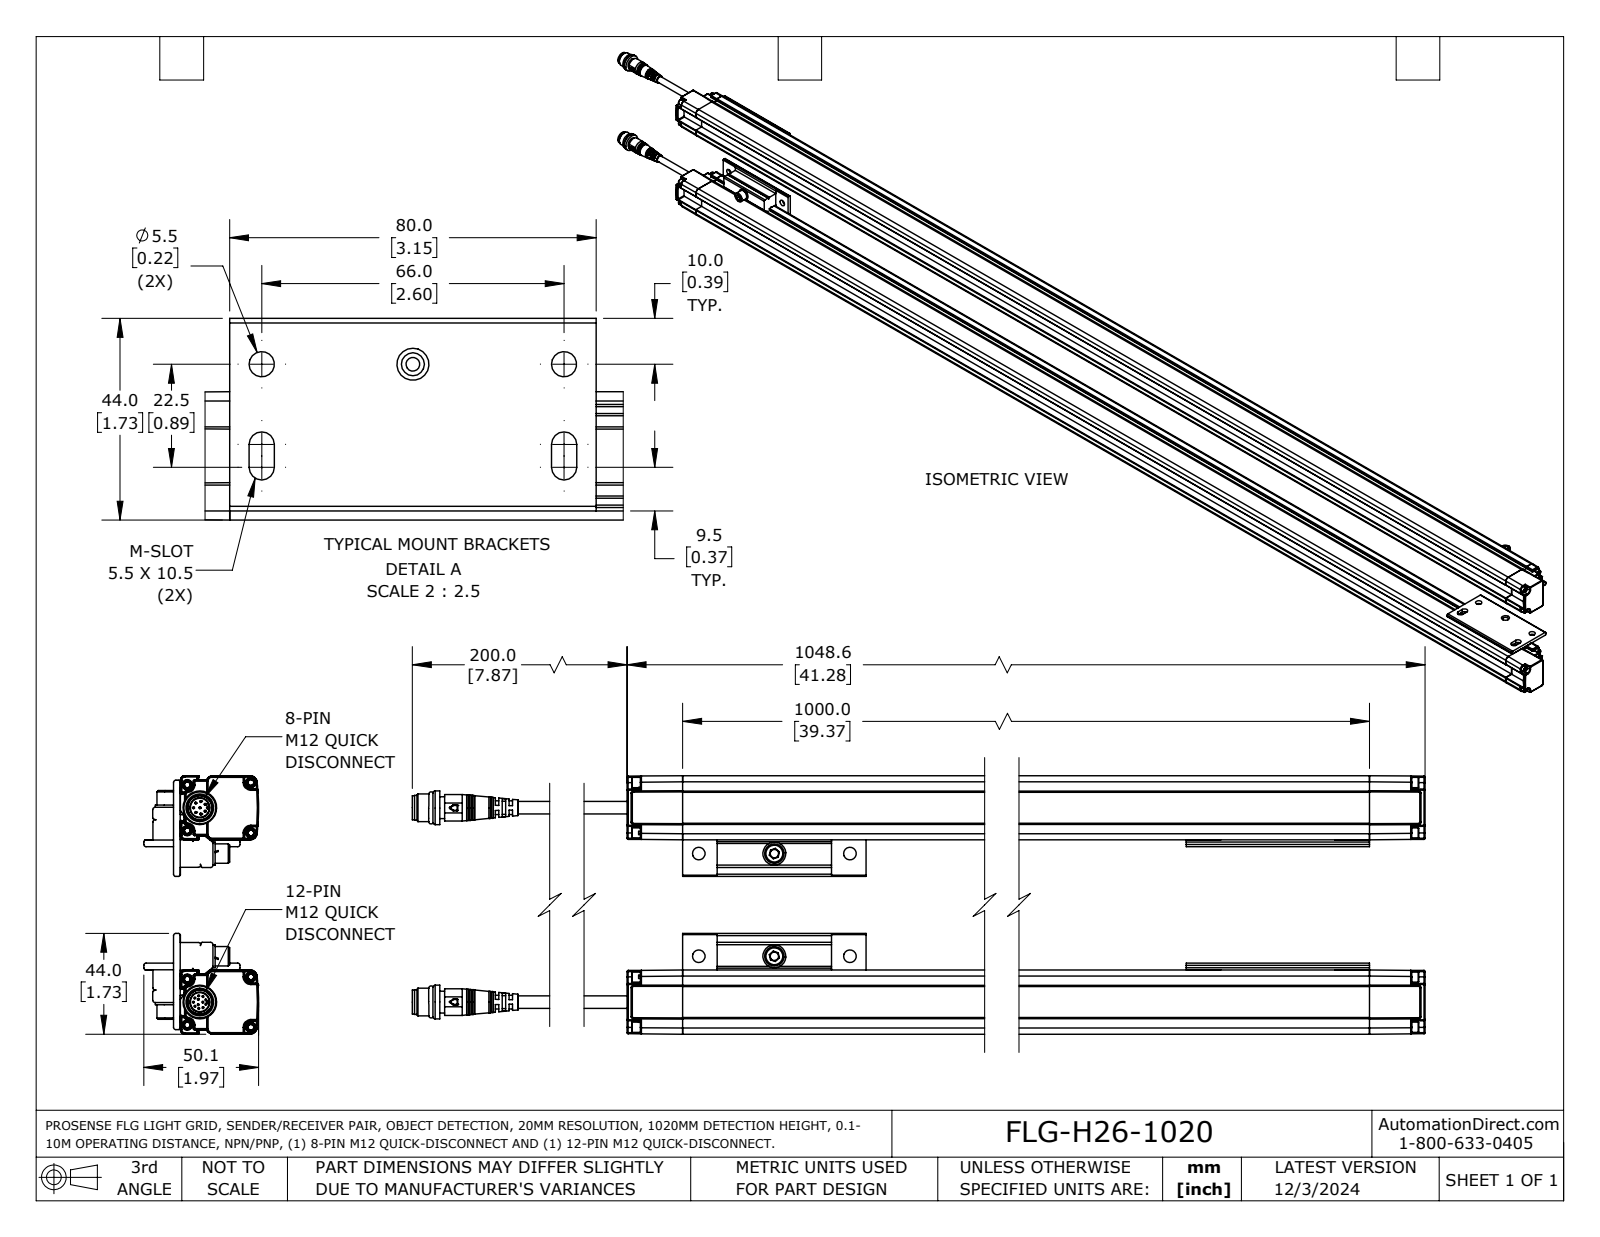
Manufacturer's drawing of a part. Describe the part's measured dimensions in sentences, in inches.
The part is named "FLG-H26-1020". Its 3-D file was written by "SolidWorks 2023 (AUTOMOTIVE_DESIGN)". It is 10 solids with 1668 faces: 816 planar, 456 cylindrical and 396 other. Overall it measures 44.904 by 4.441 by 1.972 inches. Its volume is 103.7 cubic inches and its surface area 658.6 square inches. Round holes: 16 of diameter 0.016, 6 of diameter 0.217, 4 of diameter 0.098, 3 of diameter 0.197, 2 of diameter 0.327. Round bosses or shafts: 20 of diameter 0.031, 8 of diameter 0.177, 8 of diameter 0.118, 4 of diameter 0.217, 4 of diameter 0.059, 3 of diameter 0.394, 3 of diameter 0.335, 3 of diameter 0.146. Partial cylindrical surfaces (rounded edges, fillets, slot ends): 142 of radius 0.02, 40 of radius 0.039, 20 of radius 0.01, 12 of radius 0.008, 12 of radius 0.012, 12 of radius 0.108, 6 of radius 0.1, 4 of radius 0.049. The main face-to-face distances are 3.339, 1.102, 0.071, 0.285, 0.817, 0.97, 2.236, 4.441, 1.041, 0.215. The hole center spacings are 0.108, 1.299, 0.163, 0.979, 2.191, 0.215, 1.764, 2.598.
